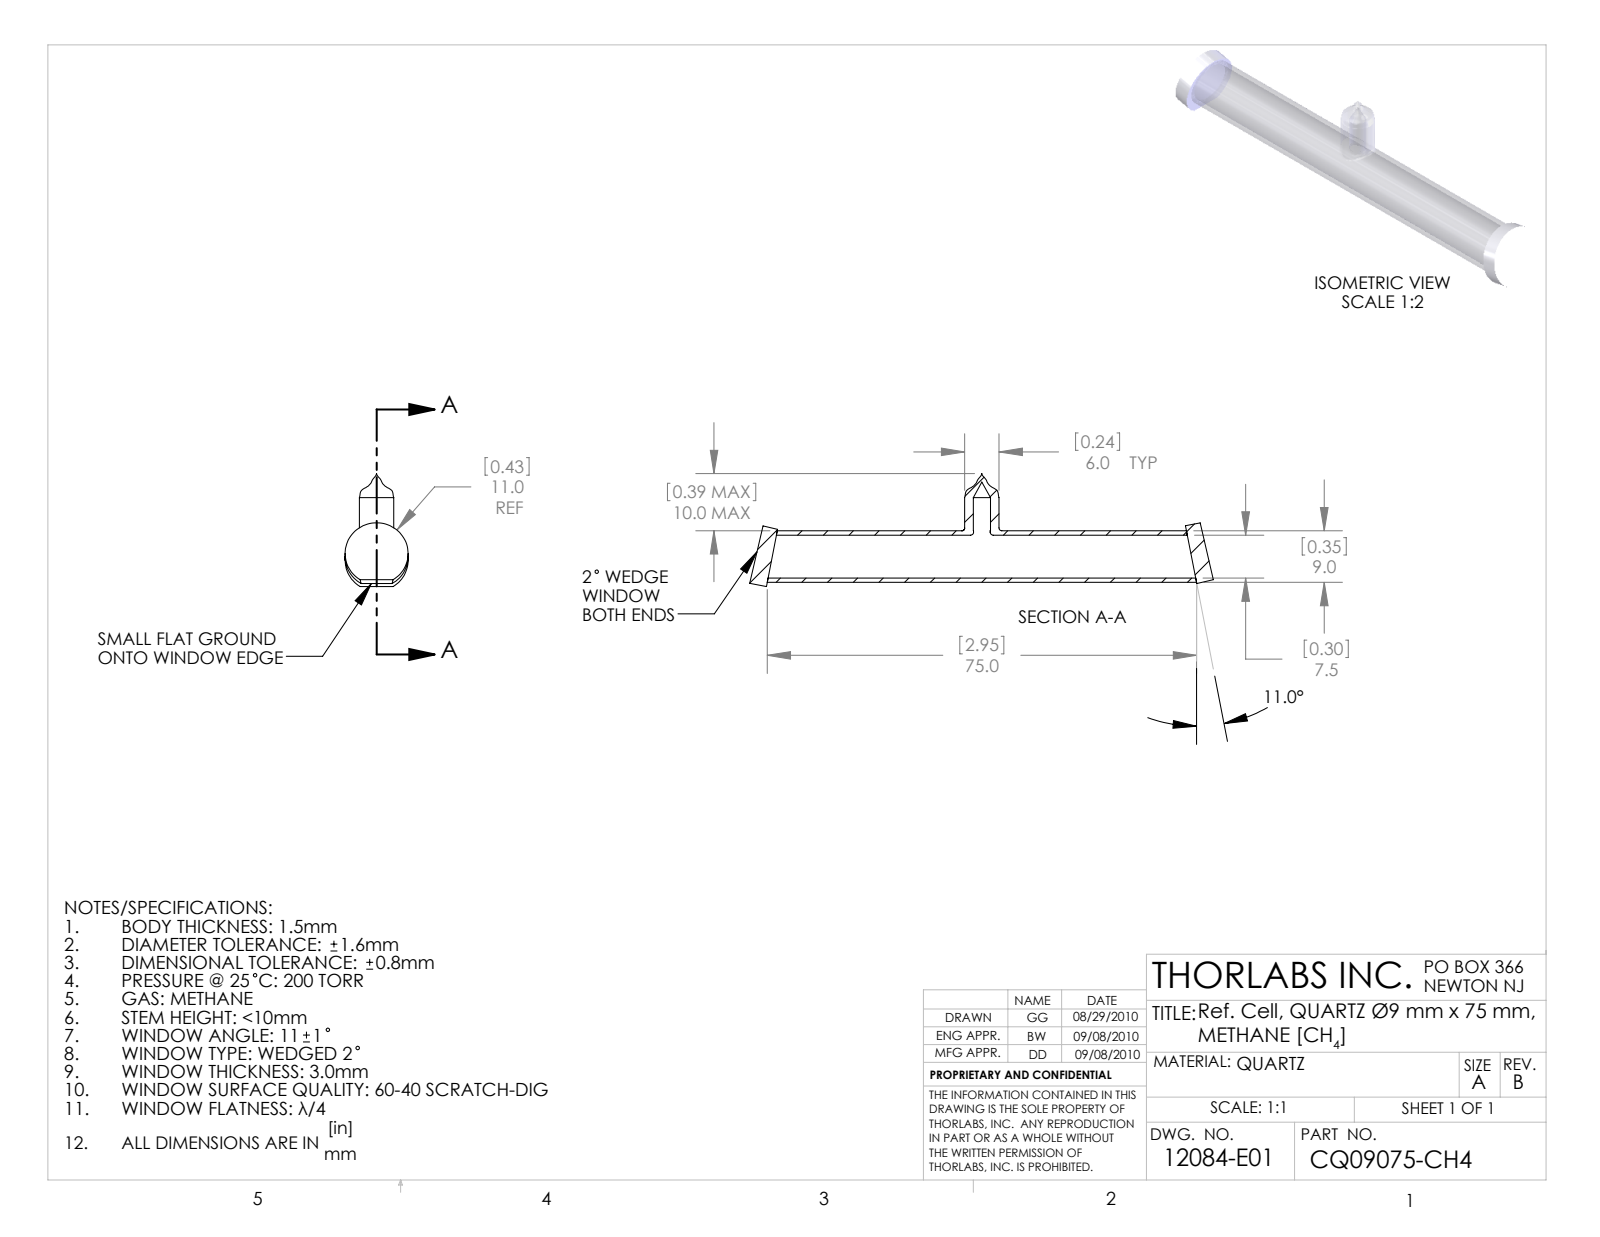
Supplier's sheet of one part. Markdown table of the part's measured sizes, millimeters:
| quantity | value |
| --- | --- |
| part name | 12084-E0W |
| STEP written by | SolidWorks 2009 (AUTOMOTIVE_DESIGN) |
| units | millimeters |
| bodies | 3 solids, 33 faces (8 planar, 17 cylindrical, 8 other) |
| overall size | 80.97 × 19.74 × 11 |
| volume | 2 106 mm³ |
| surface area | 4 607 mm² |
| round holes (diameter × count) | 2.91 × 1, 3 × 1, 7.5 × 1 |
| round bosses / shafts (diameter × count) | 11 × 2, 9 × 1, 6 × 1 |
